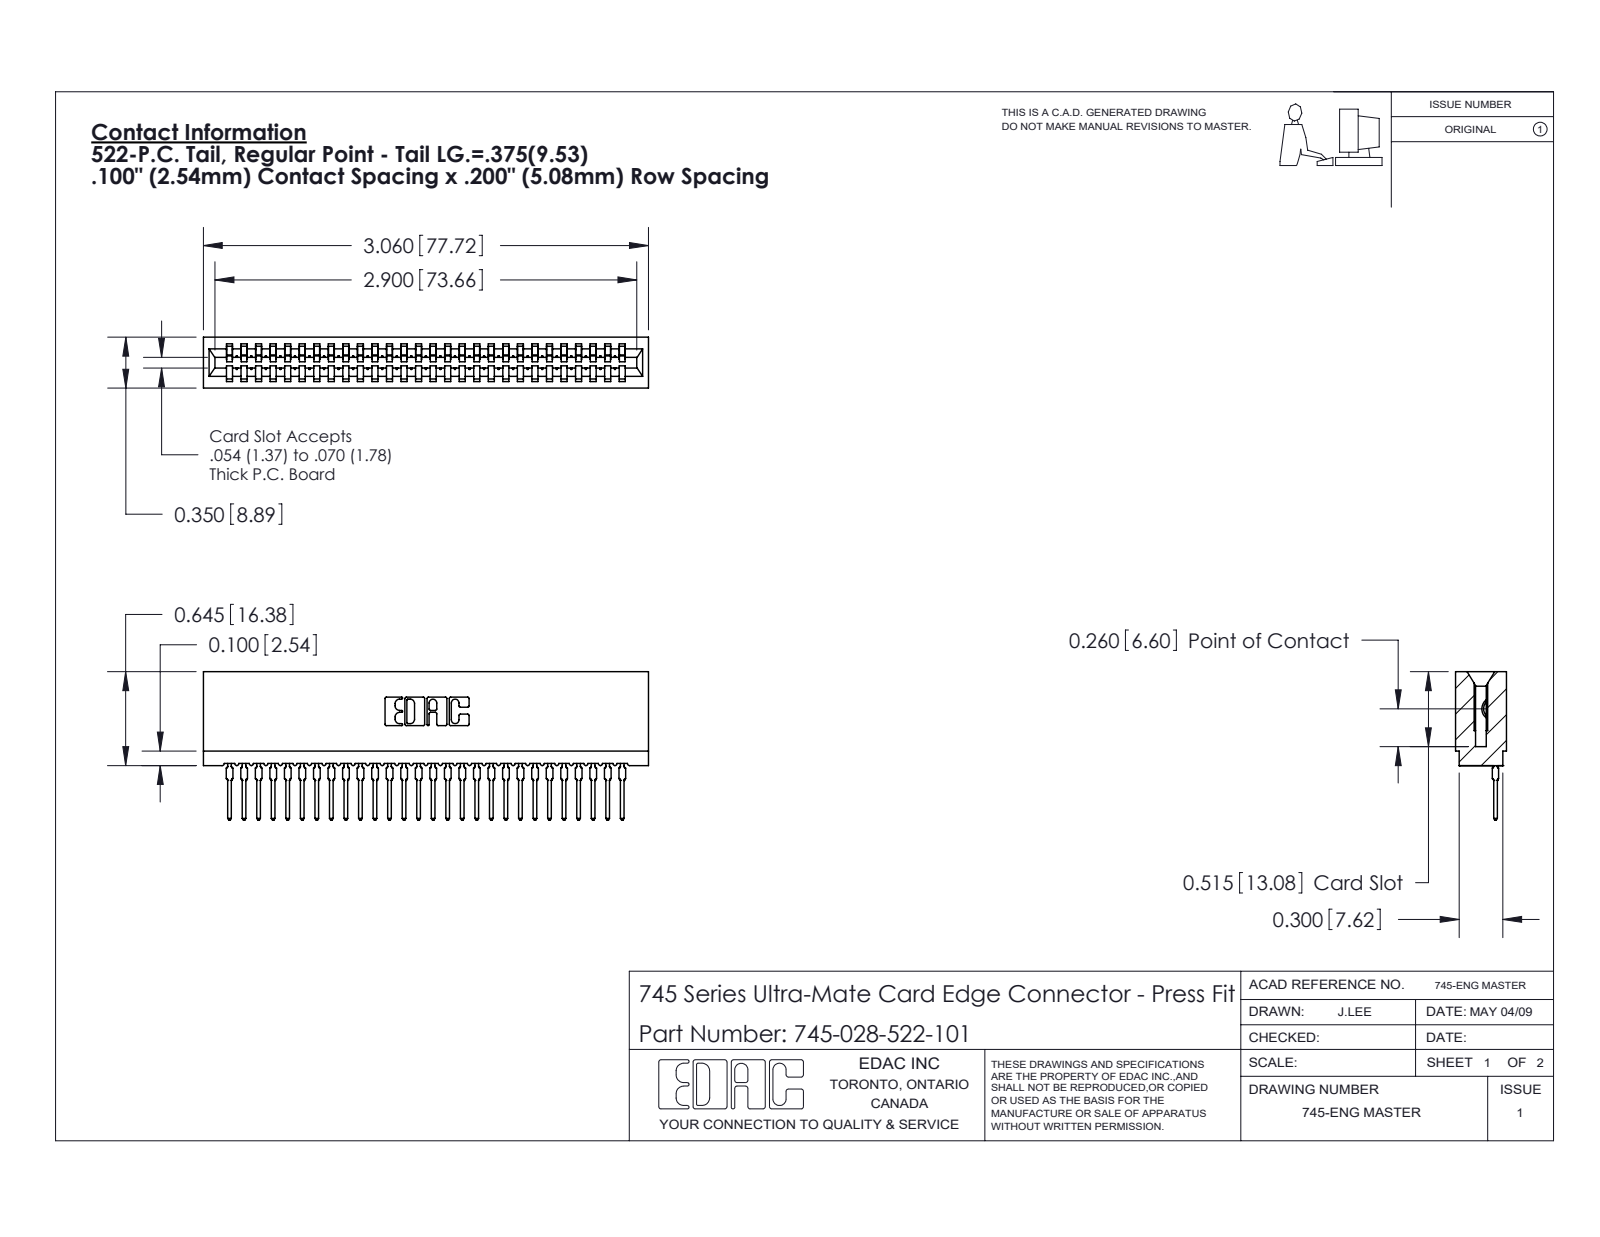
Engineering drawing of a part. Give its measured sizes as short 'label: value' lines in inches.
name: 745-028-522-101; 745-292-001_522; 745 Part_Insulator Option - 01
written by: SolidWorks 2020 (CONFIG_CONTROL_DESIGN)
unit: in
bodies: 29 solids, 3231 faces (1931 planar, 572 cylindrical, 728 other)
size: 3.06 × 1.021 × 0.35
volume: 0.417 in³; area: 19.44 in²
rounds: 56× R0.015, 56× R0.021, 22× R0.01, 6× R0.007, 6× R0.031, 4× R0.005, 4× R0.011, 3× R0.026
face distances: 0.35, 0.1, 0.2, 0.138, 0.212, 0.045, 0.305, 0.093, 0.167, 0.3
